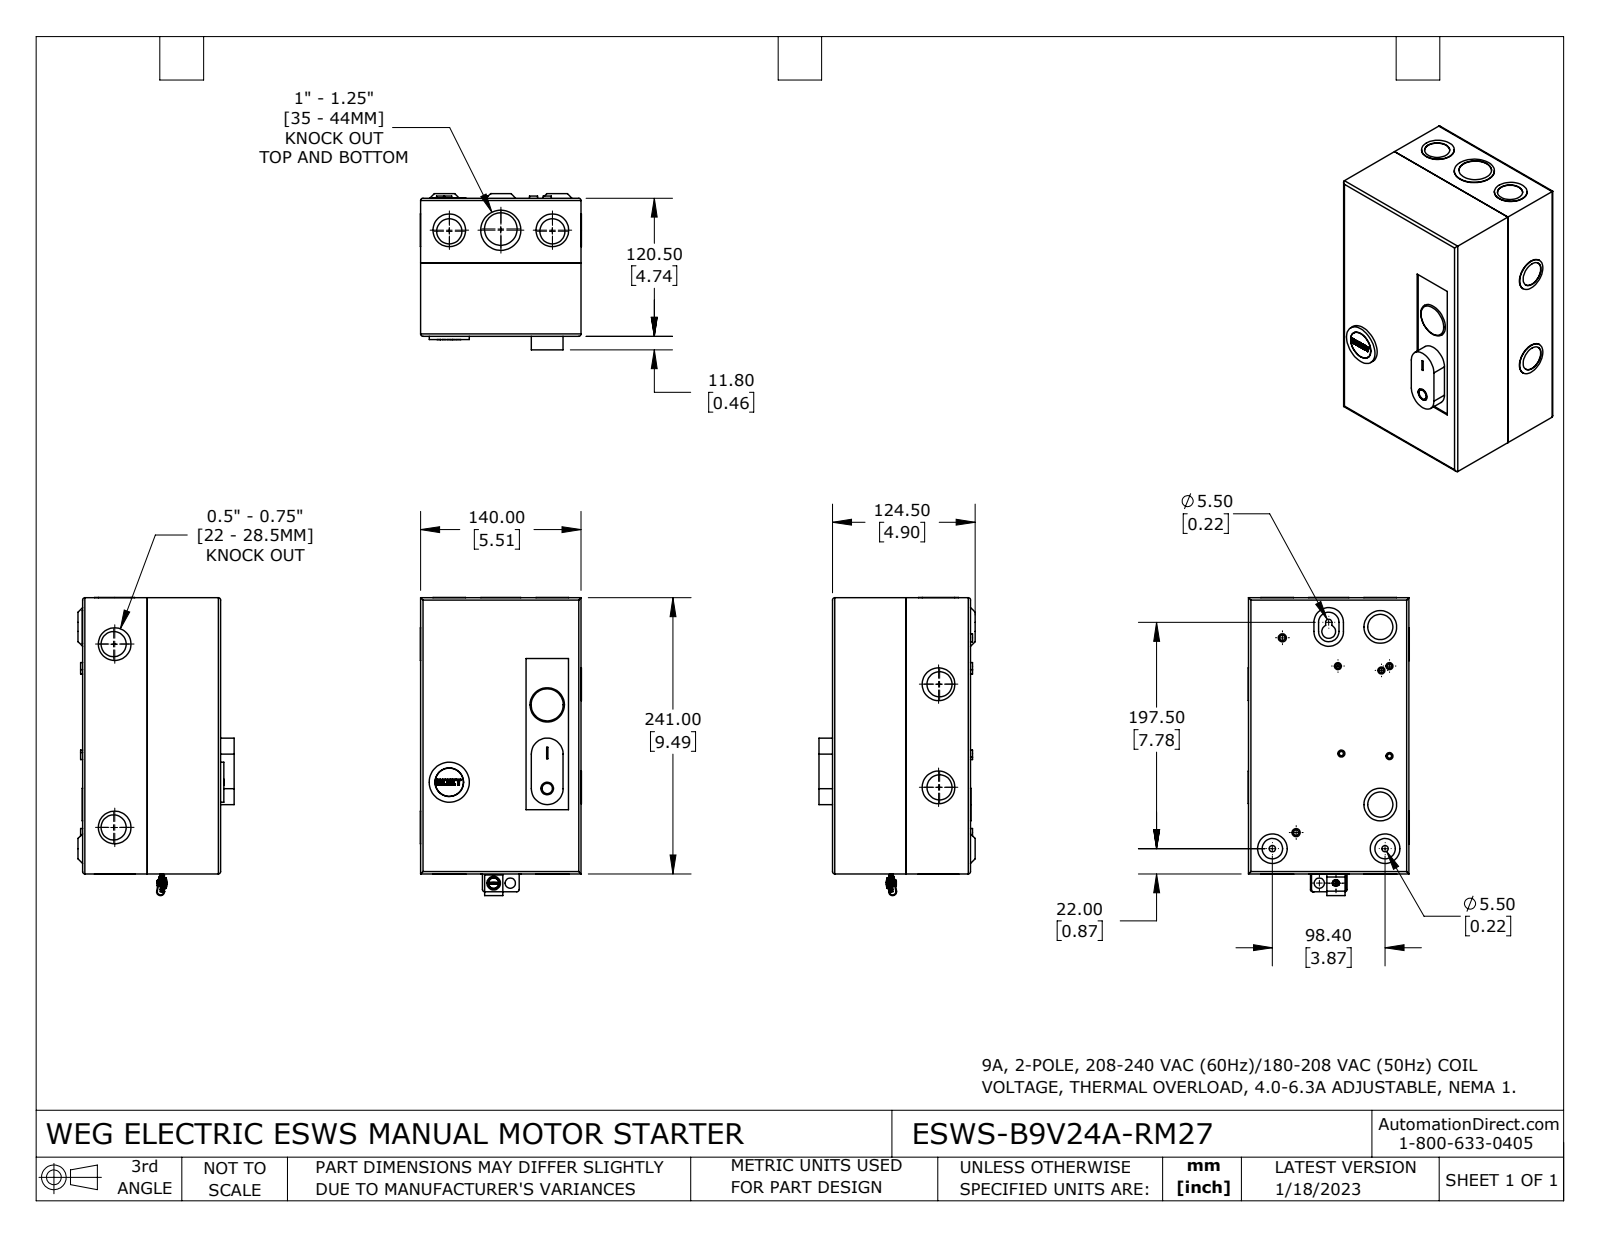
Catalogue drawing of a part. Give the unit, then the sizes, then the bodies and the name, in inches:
Units: inches
Overall size (bounding box): 10.248 × 5.535 × 5.366
Round holes (diameter × count): ⌀0.146 ×5, ⌀0.864 ×4, ⌀0.183 ×2, ⌀0.217 ×2, ⌀0.354 ×2, ⌀0.864 ×2, ⌀0.866 ×2, ⌀0.886 ×2, ⌀0.256 ×1, ⌀0.303 ×1, ⌀0.433 ×1, ⌀0.469 ×1
Round bosses / shafts (diameter × count): ⌀1.124 ×6, ⌀0.24 ×5, ⌀1.122 ×2, ⌀0.278 ×2, ⌀1.38 ×1, ⌀1.378 ×1, ⌀1.193 ×1, ⌀1.148 ×1
Partial cylindrical surfaces — rounded edges, fillets, slot ends (radius × count): R0.004 ×34, R0.079 ×13, R0.031 ×4, R0.108 ×3, R0.059 ×2, R0.075 ×2, R0.122 ×2, R0.138 ×2
Main face-to-face distances: 0.047, 4.697, 5.465, 4.65, 9.441, 4.744, 5.417, 5.512, 0.071, 0.063
Hole centre spacings: 0.571, 1.378, 1.773, 3.387, 3.543, 4.921, 5.995, 7.484
Volume: 16.23 in³ · Surface area: 585.2 in²
Bodies: 7 solids, 435 faces (168 planar, 230 cylindrical, 37 other)
Part name (STEP PRODUCT): ESWS-B9V24A-RM27
STEP written by: SolidWorks 2021 (CONFIG_CONTROL_DESIGN)
